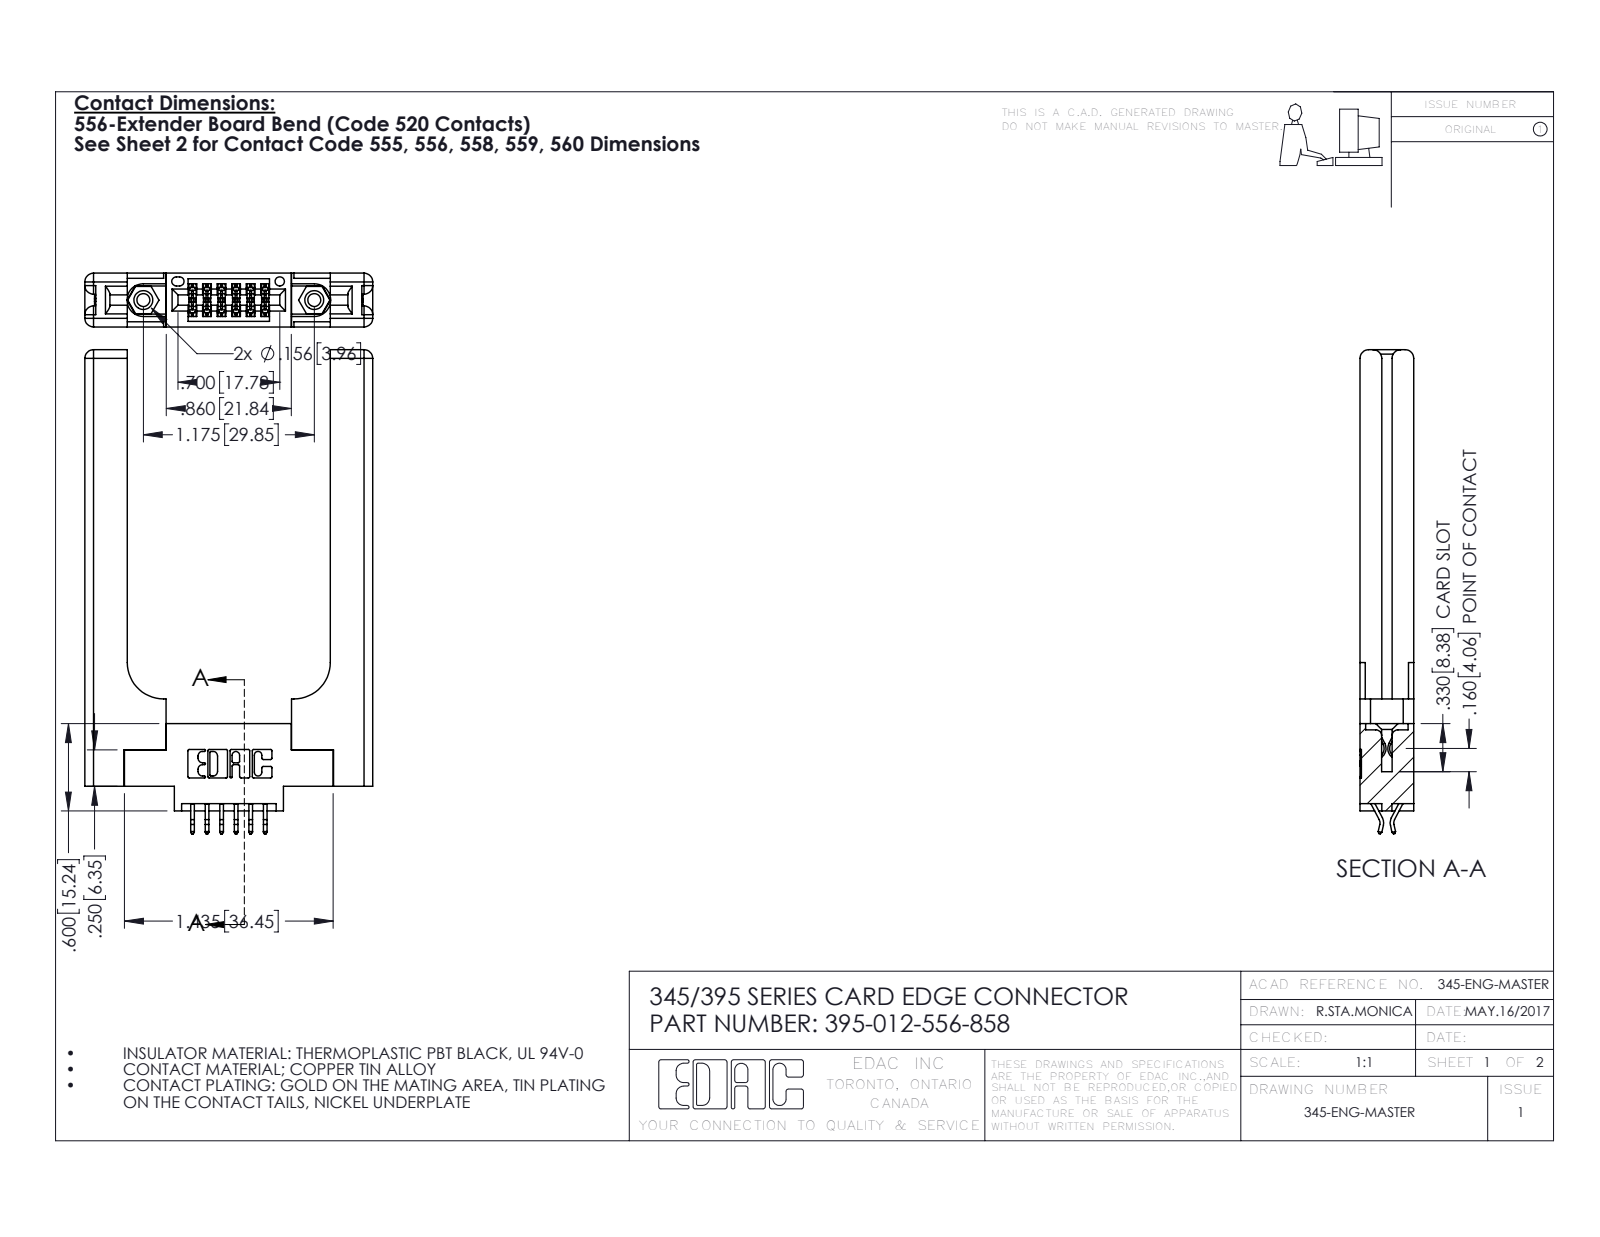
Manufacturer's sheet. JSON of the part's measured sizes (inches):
{"part_name": "395-012-556-858; 345-292-001_556 Tail; 345-250-001_345-250-001-102; 345-220-058_345-220-058 (+1 more)", "step_written_by": "SolidWorks 2016 (CONFIG_CONTROL_DESIGN)", "units": "inches", "bodies": {"solids": 17, "faces": 1058, "planar": 676, "cylindrical": 322, "other": 60}, "overall_size": [3.327, 1.979, 0.37], "volume_in3": 0.788, "surface_area_in2": 17.13, "round_holes": [[0.089, 2], [0.125, 2], [0.156, 2], [0.064, 1]], "round_bosses_or_shafts": [[0.155, 2]], "partial_cylinders_radius": [[0.01, 22], [0.006, 18], [0.06, 16], [0.007, 6], [0.031, 6], [0.026, 3], [0.01, 2], [0.014, 2]], "face_to_face_distances": [0.37, 0.15, 0.22, 0.072, 0.077, 0.148, 1.396, 0.298, 0.071, 0.292], "hole_center_spacings": [0.27, 0.946, 1.175]}
